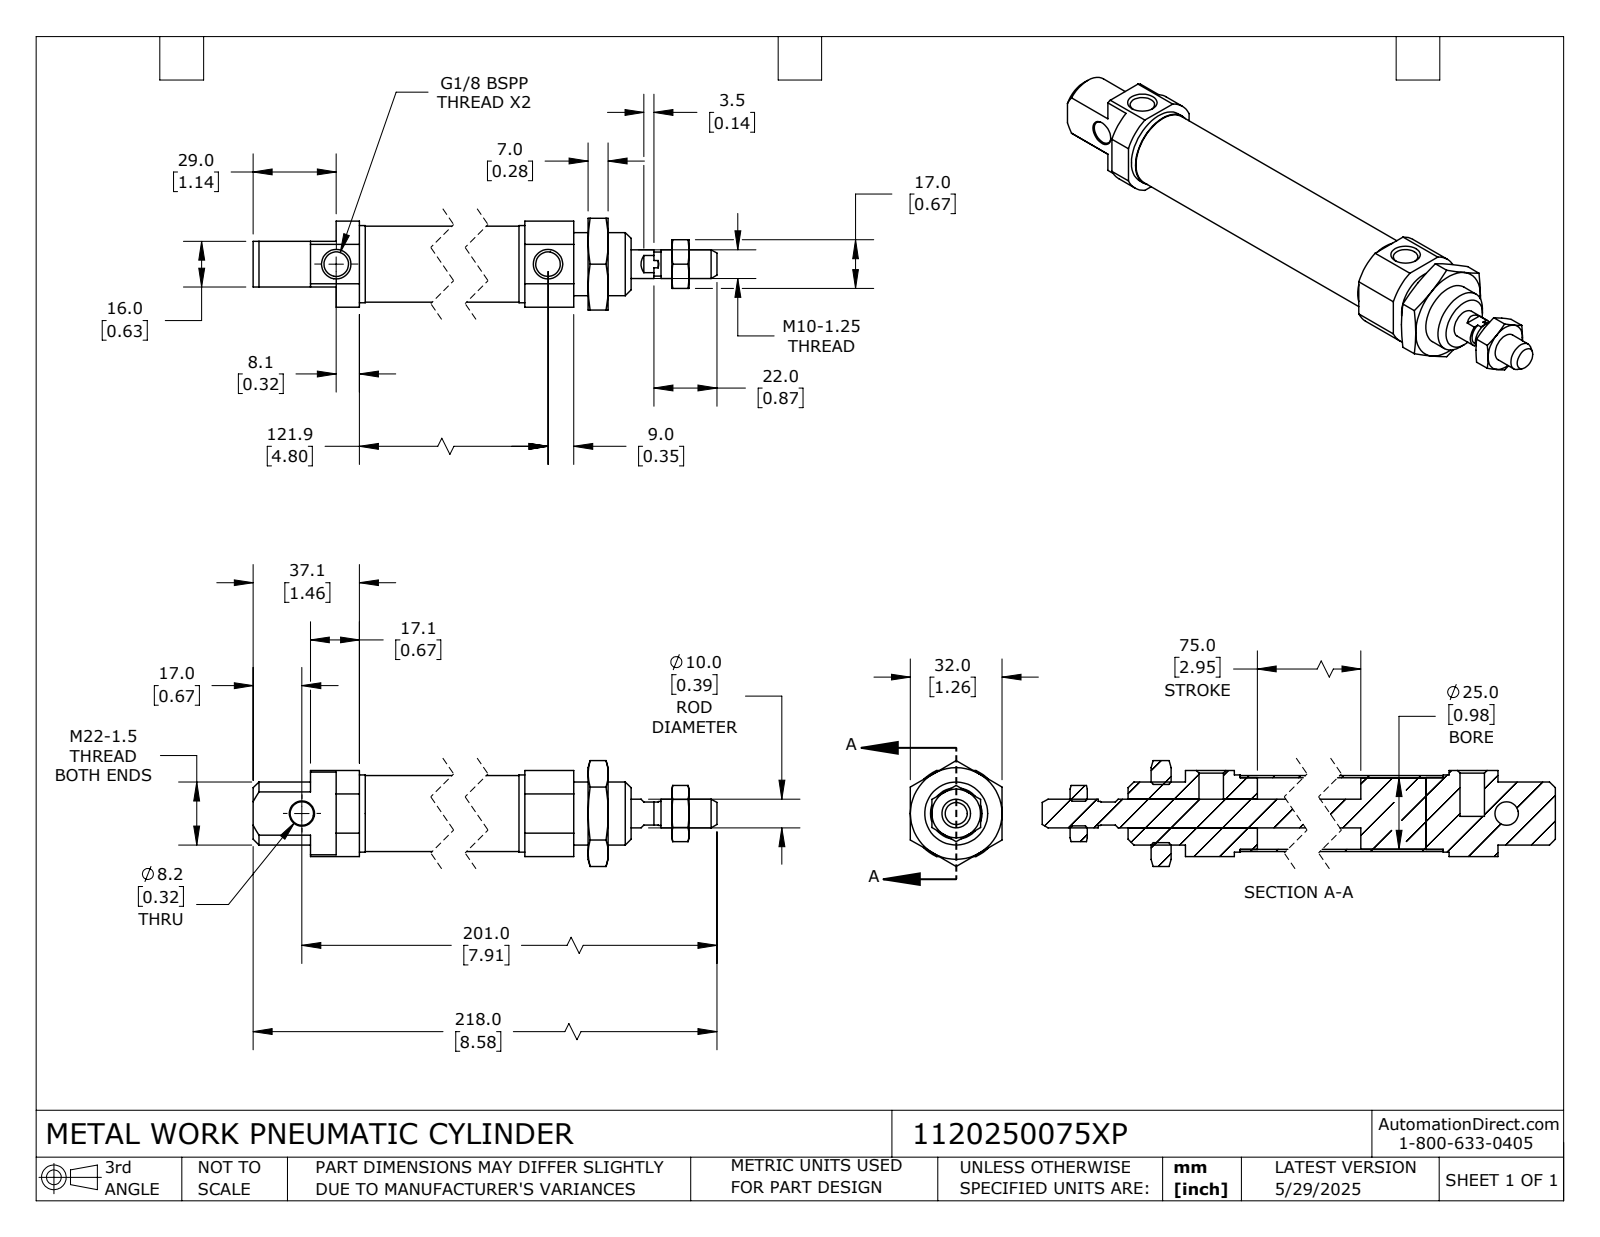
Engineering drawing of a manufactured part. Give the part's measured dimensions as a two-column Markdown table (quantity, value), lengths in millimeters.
| quantity | value |
| --- | --- |
| part name | 1120250075XP; 1120250075XP_ROD; 1120250075XP_BODY |
| STEP written by | SolidWorks 2024 (CONFIG_CONTROL_DESIGN) |
| units | millimeters |
| bodies | 6 solids, 144 faces (54 planar, 44 cylindrical, 46 other) |
| overall size | 218 × 36.95 × 32 |
| volume | 75 120 mm³ |
| surface area | 41 053 mm² |
| round holes (diameter × count) | 8.57 × 2, 8.2 × 1, 8.65 × 1, 20.38 × 1, 25 × 1 |
| round bosses / shafts (diameter × count) | 27 × 1, 26.52 × 1, 25.15 × 1, 22 × 1, 10 × 1, 8.4 × 1 |
| partial cylindrical surfaces (radius × count) | 16.5 × 1 |
| main face-to-face distances | 7, 8, 37.1, 23, 30, 142.9, 122.9, 25.1, 16, 105.8 |
| hole center spacings | 130 |
